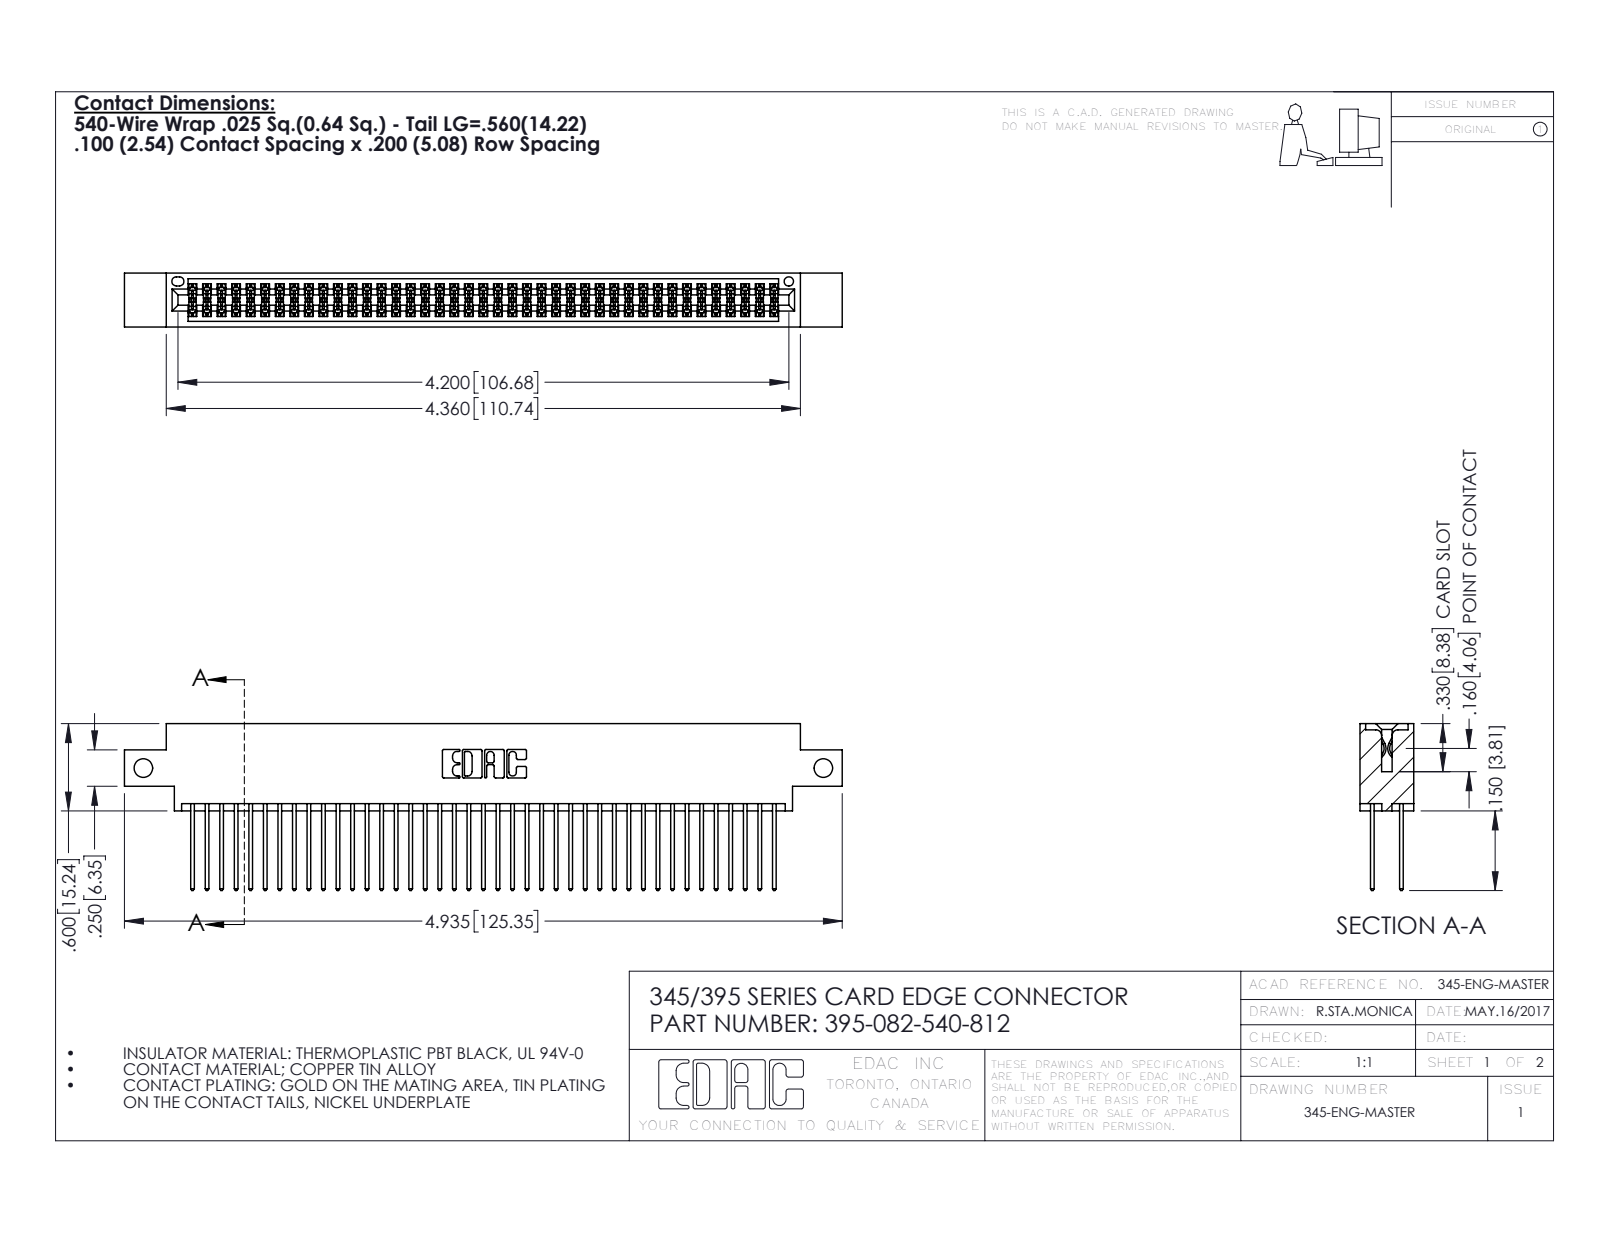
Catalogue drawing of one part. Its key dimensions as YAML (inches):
part_name: "345 Part_0.170 Offset - Side Mount; 345-292-001_345-293-140; 395-082-540-812"
step_written_by: "SolidWorks 2016 (CONFIG_CONTROL_DESIGN)"
units: inches
bodies: {solids: 83, faces: 4230, planar: 2790, cylindrical: 1440, other: 0}
overall_size: [4.935, 1.147, 0.37]
volume: 0.749
surface_area: 30.35
round_holes:
  - {diameter: 0.128, count: 2}
  - {diameter: 0.064, count: 1}
partial_cylinders:
  - {radius: 0.006, count: 123}
  - {radius: 0.01, count: 82}
  - {radius: 0.01, count: 22}
  - {radius: 0.007, count: 6}
  - {radius: 0.031, count: 6}
  - {radius: 0.026, count: 3}
  - {radius: 0.014, count: 2}
  - {radius: 0.019, count: 2}
face_to_face_distances: [0.298, 0.072, 0.2, 0.098, 0.272, 0.025, 0.37, 0.225, 0.175, 0.149]
hole_center_spacings: [4.675]
